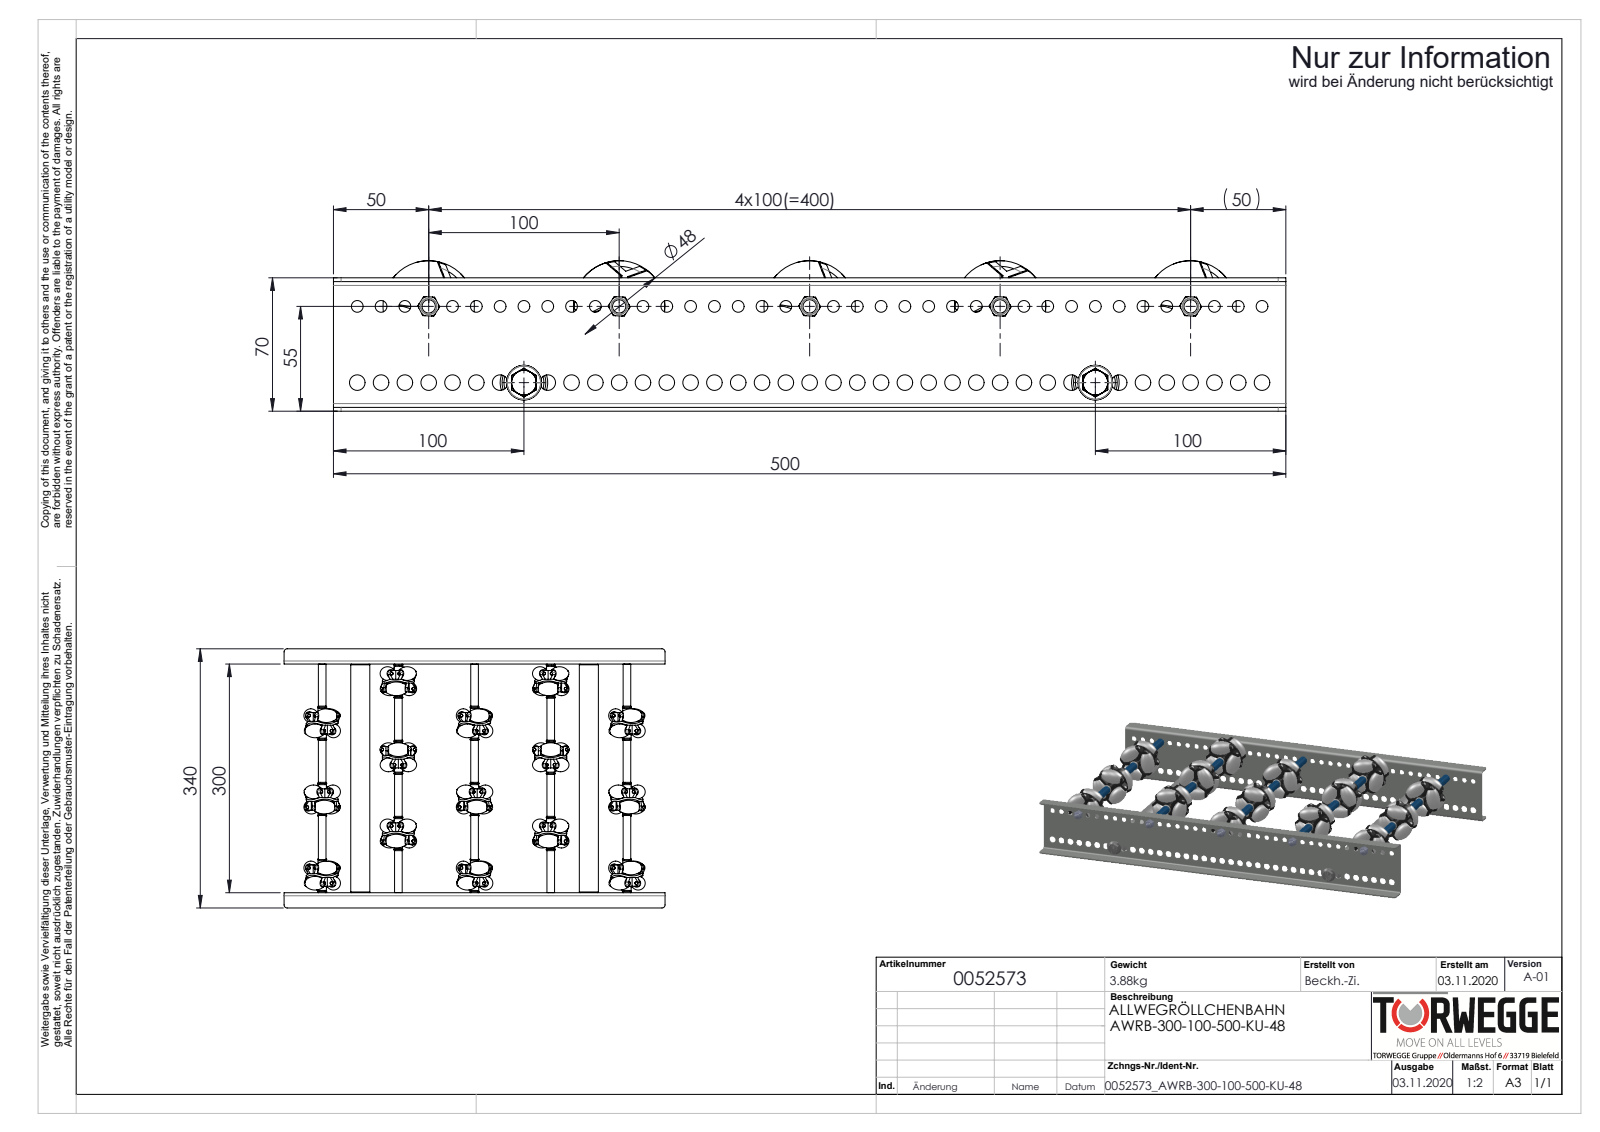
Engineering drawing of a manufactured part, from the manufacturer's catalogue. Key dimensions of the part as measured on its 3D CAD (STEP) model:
Part name (STEP PRODUCT): 0052573; S100994_Sperrzahnschraube_M08x16-8.8-A2K; 0019719_Gewindestange-M6_L=320; Profil-RB-20x70x20x2_S100208_U-PROFIL-20-70-20-2-RB-L=500 (+8 more)
STEP written by: SolidWorks 2020 (AUTOMOTIVE_DESIGN)
Units: millimetres
Bodies: 267 solids, 5002 faces (1680 planar, 1978 cylindrical, 1344 other)
Overall size (bounding box): 500 × 340 × 79
Volume: 1 031 000 mm³ · Surface area: 760 654 mm²
Round holes (diameter × count): ⌀3.7 ×90, ⌀4.2 ×90, ⌀6.2 ×39, ⌀8.2 ×39, ⌀4.92 ×5, ⌀6.5 ×5, ⌀8.4 ×5, ⌀6.8 ×2, ⌀21 ×2
Round bosses / shafts (diameter × count): ⌀4 ×90, ⌀3.7 ×71, ⌀8 ×7, ⌀42 ×5, ⌀11 ×5, ⌀10 ×5, ⌀7 ×5, ⌀6 ×5
Partial cylindrical surfaces — rounded edges, fillets, slot ends (radius × count): R4 ×8, R23.55 ×5, R2 ×4
Main face-to-face distances: 2, 302, 68, 300, 304, 14.75, 70, 66, 3, 11.75
Hole centre spacings: 36.06, 36.05, 12.5, 25, 37.5, 50, 62.5, 75
